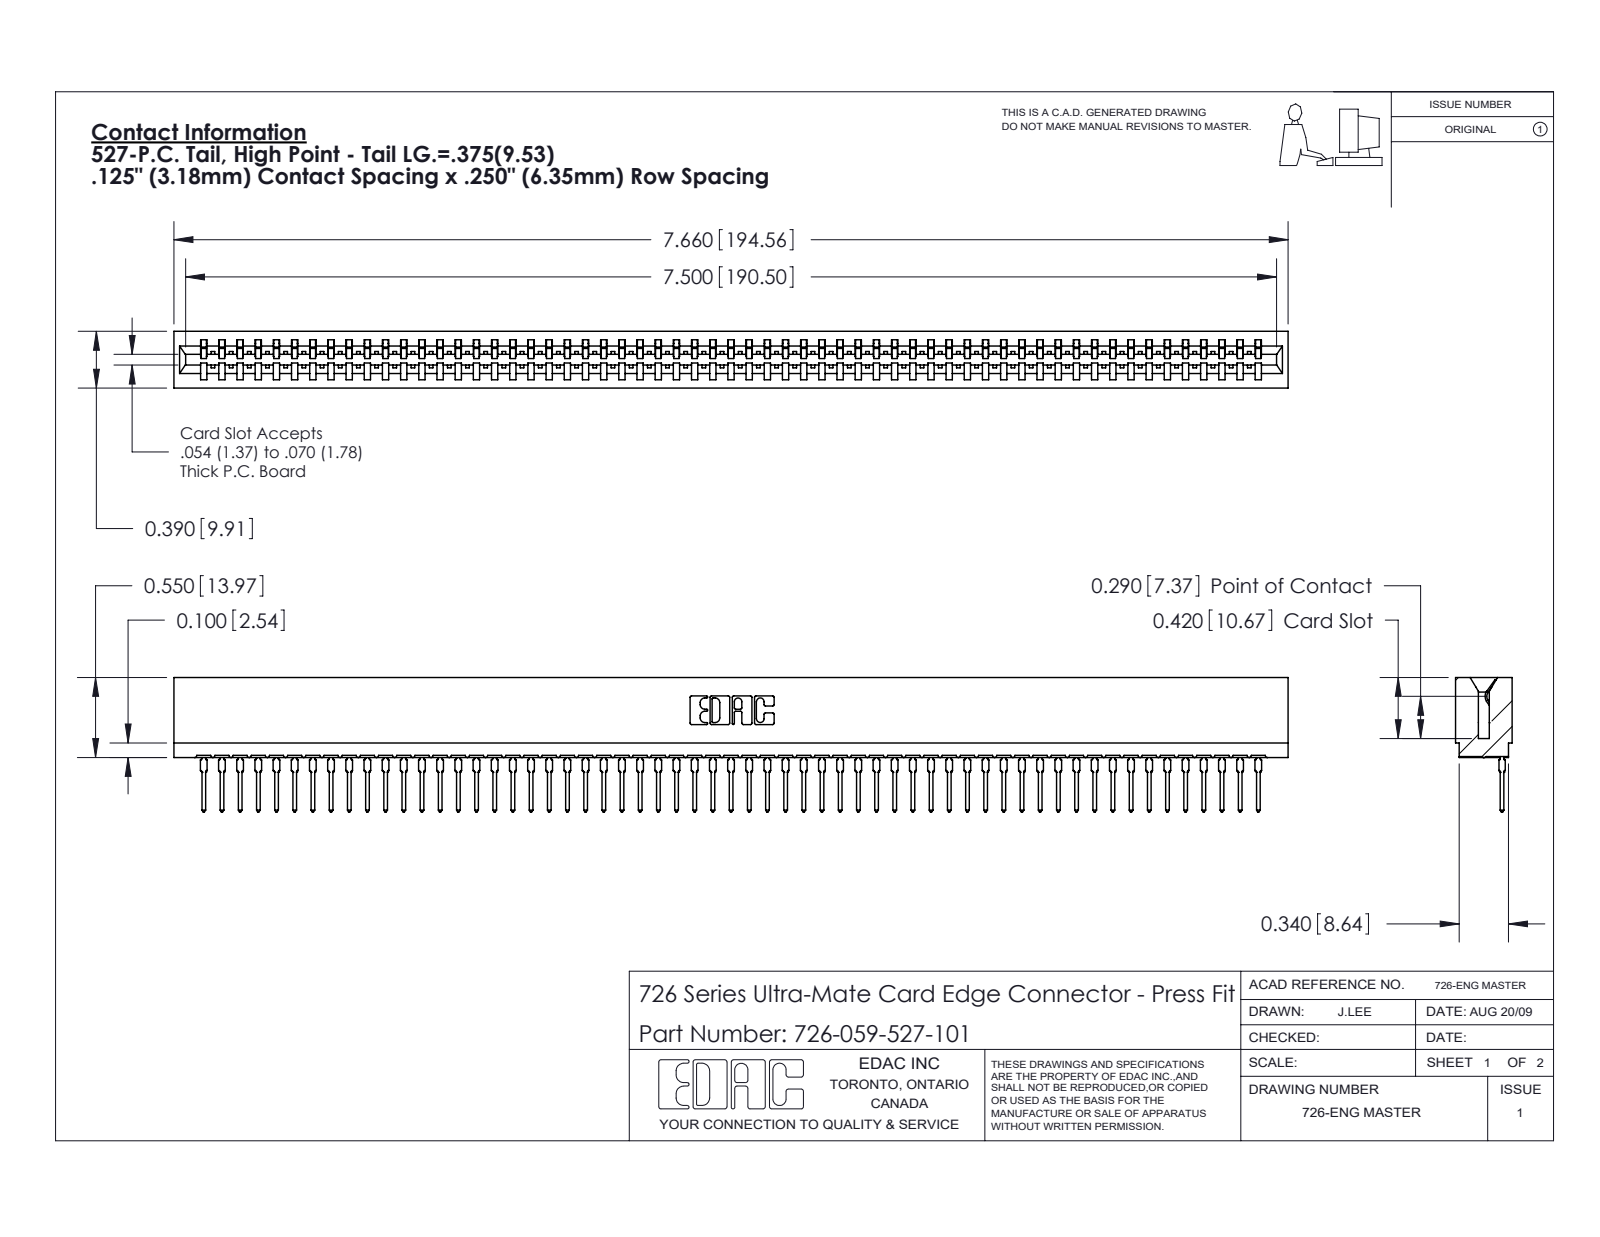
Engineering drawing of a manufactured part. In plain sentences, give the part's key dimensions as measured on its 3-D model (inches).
The part is named "726-059-527-101; 746-292-001_527; 726 Part_.515 Slot Depth - 01". Its 3-D file was written by "SolidWorks 2020 (CONFIG_CONTROL_DESIGN)". It is 60 solids with 6469 faces: 3772 planar, 1163 cylindrical and 1534 other. Overall it measures 7.66 by 0.924 by 0.39 inches. Its volume is 1.058 cubic inches and its surface area 41.91 square inches. Partial cylindrical surfaces (rounded edges, fillets, slot ends): 118 of radius 0.021, 60 of radius 0.015, 22 of radius 0.01, 6 of radius 0.007, 6 of radius 0.031, 4 of radius 0.005, 4 of radius 0.011, 3 of radius 0.026. The main face-to-face distances are 0.057, 0.333, 0.39, 0.025, 0.307, 0.25, 0.275, 0.083, 0.365, 0.032.
